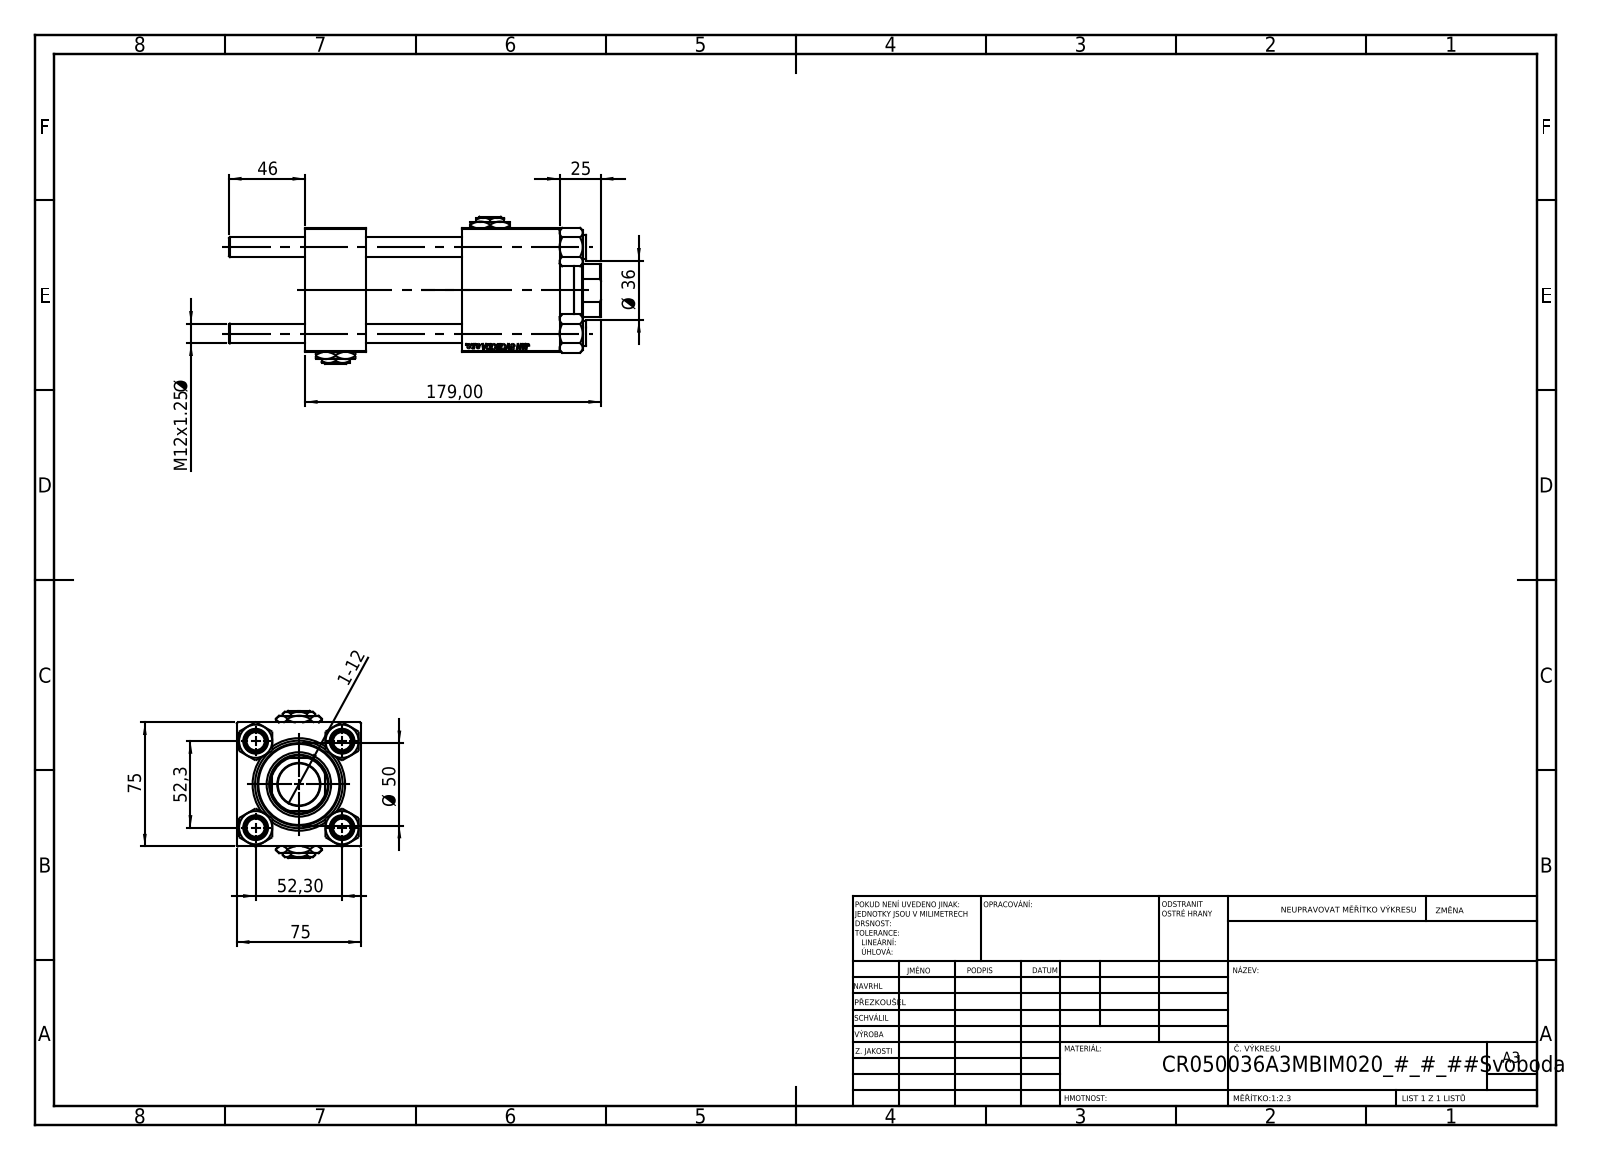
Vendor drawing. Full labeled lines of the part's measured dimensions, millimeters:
Part name (STEP PRODUCT): Zatka_pro_OIL_PORT; NUT_M5; V215CR_BODY_A; V215_VC_A (+2 more)
STEP written by: SolidWorks 2019 (CONFIG_CONTROL_DESIGN)
Units: millimetres
Bodies: 13 solids, 1233 faces (567 planar, 88 cylindrical, 578 other)
Overall size (bounding box): 225 × 89 × 75
Volume: 714 043 mm³ · Surface area: 176 424 mm²
Round holes (diameter × count): ⌀12 ×4, ⌀7 ×2, ⌀20.96 ×2, ⌀30 ×2, ⌀25.5 ×1, ⌀36 ×1, ⌀39 ×1, ⌀41 ×1, ⌀53 ×1
Round bosses / shafts (diameter × count): ⌀15 ×4, ⌀56 ×1, ⌀50 ×1
Partial cylindrical surfaces — rounded edges, fillets, slot ends (radius × count): R17.5 ×1
Main face-to-face distances: 75, 37, 95, 154, 117, 59, 58, 74.8, 125.3, 88.3
Hole centre spacings: 36.98, 52.3, 73.96, 93.5
